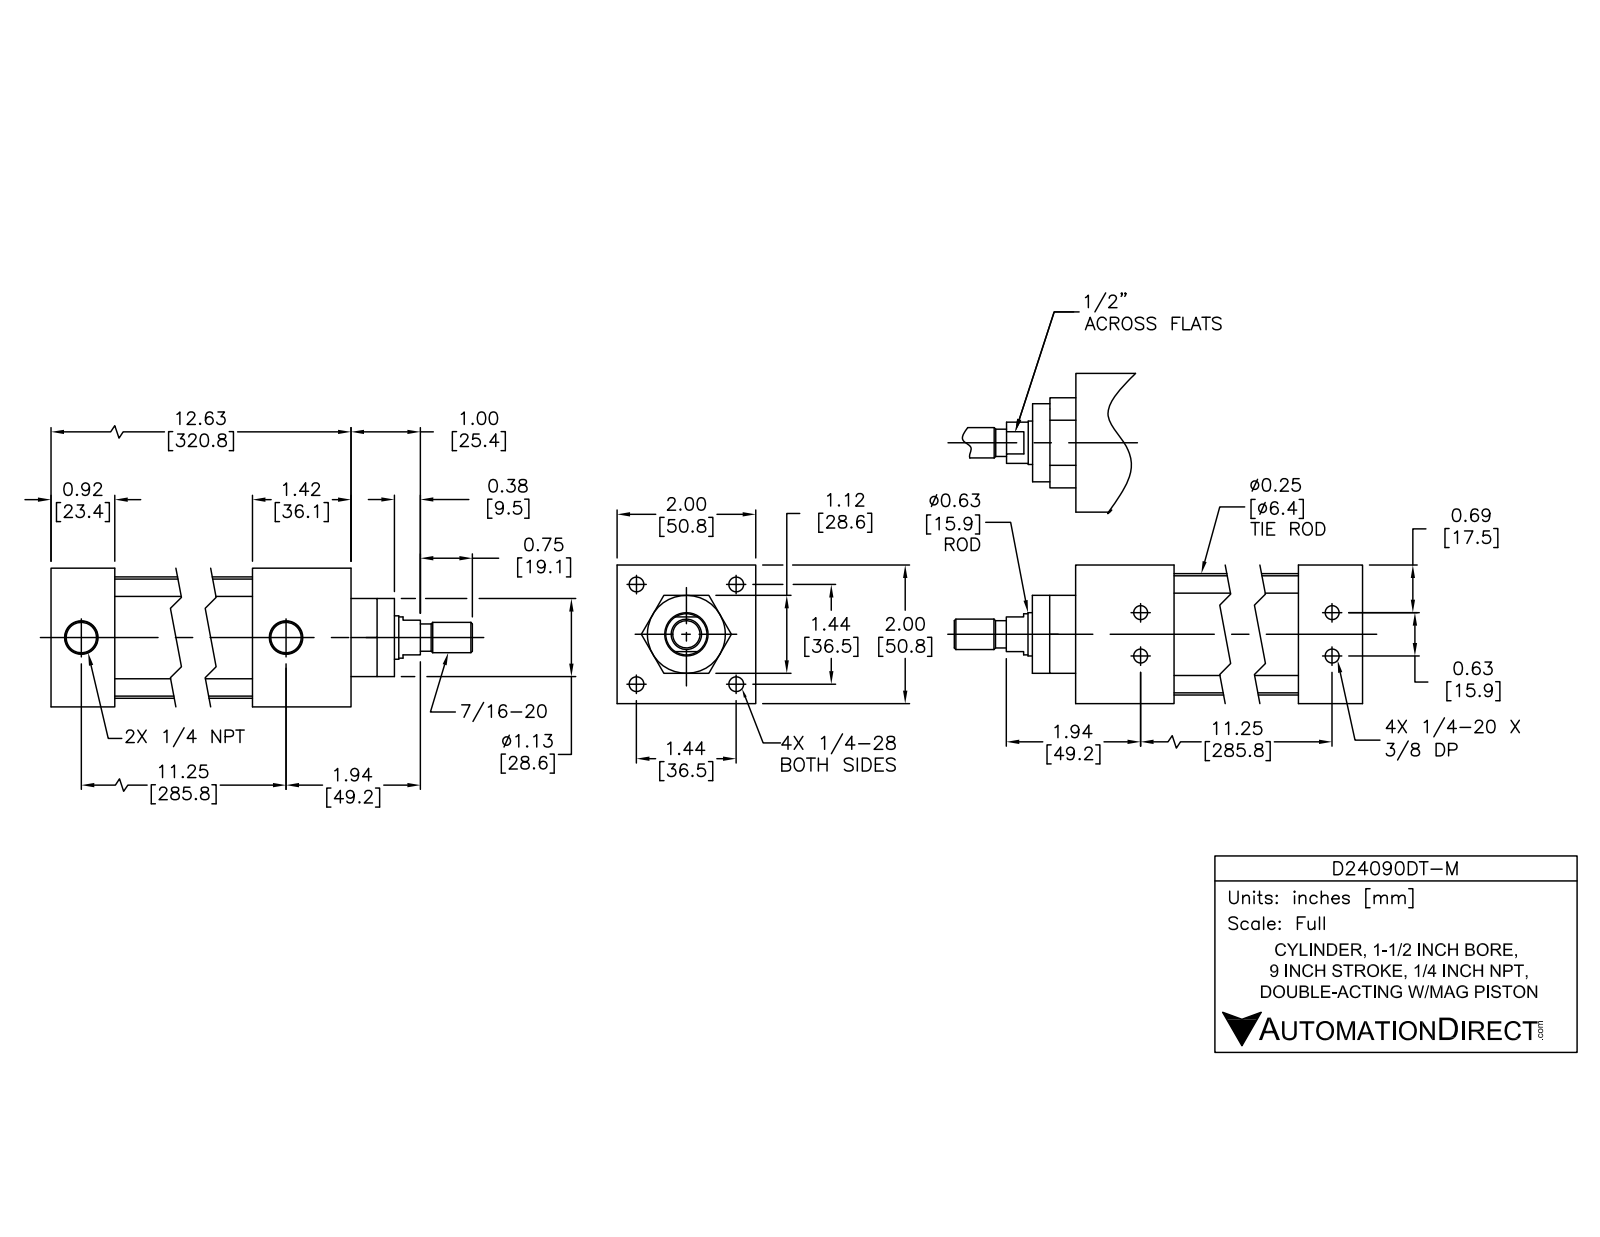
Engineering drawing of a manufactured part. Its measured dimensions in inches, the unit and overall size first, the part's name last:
Units: inches
Overall size (bounding box): 14.371 × 2 × 2
Round holes (diameter × count): ⌀0.196 ×4, ⌀0.211 ×4, ⌀0.281 ×4, ⌀0.406 ×4, ⌀0.297 ×2, ⌀0.477 ×2, ⌀0.625 ×1, ⌀0.628 ×1, ⌀1.5 ×1
Round bosses / shafts (diameter × count): ⌀0.39 ×4, ⌀0.25 ×4, ⌀0.222 ×4, ⌀1.75 ×1, ⌀1.497 ×1, ⌀1.121 ×1, ⌀0.622 ×1, ⌀0.59 ×1
Partial cylindrical surfaces — rounded edges, fillets, slot ends (radius × count): R0.2 ×4
Main face-to-face distances: 2, 12.621, 1.42, 11.201, 11.701, 10.281, 0.92, 1.121, 11.601, 10.181
Hole centre spacings: 0.313, 1.014, 1.434, 0.625, 2.028, 11.247, 11.25, 11.25
Volume: 22.56 in³ · Surface area: 227.7 in²
Bodies: 12 solids, 303 faces (99 planar, 114 cylindrical, 90 other)
Part name (STEP PRODUCT): D24090DT-M PISTON; D24090DT-M; D24090DT-M BODY
STEP written by: SolidWorks 2015 (AUTOMOTIVE_DESIGN)
